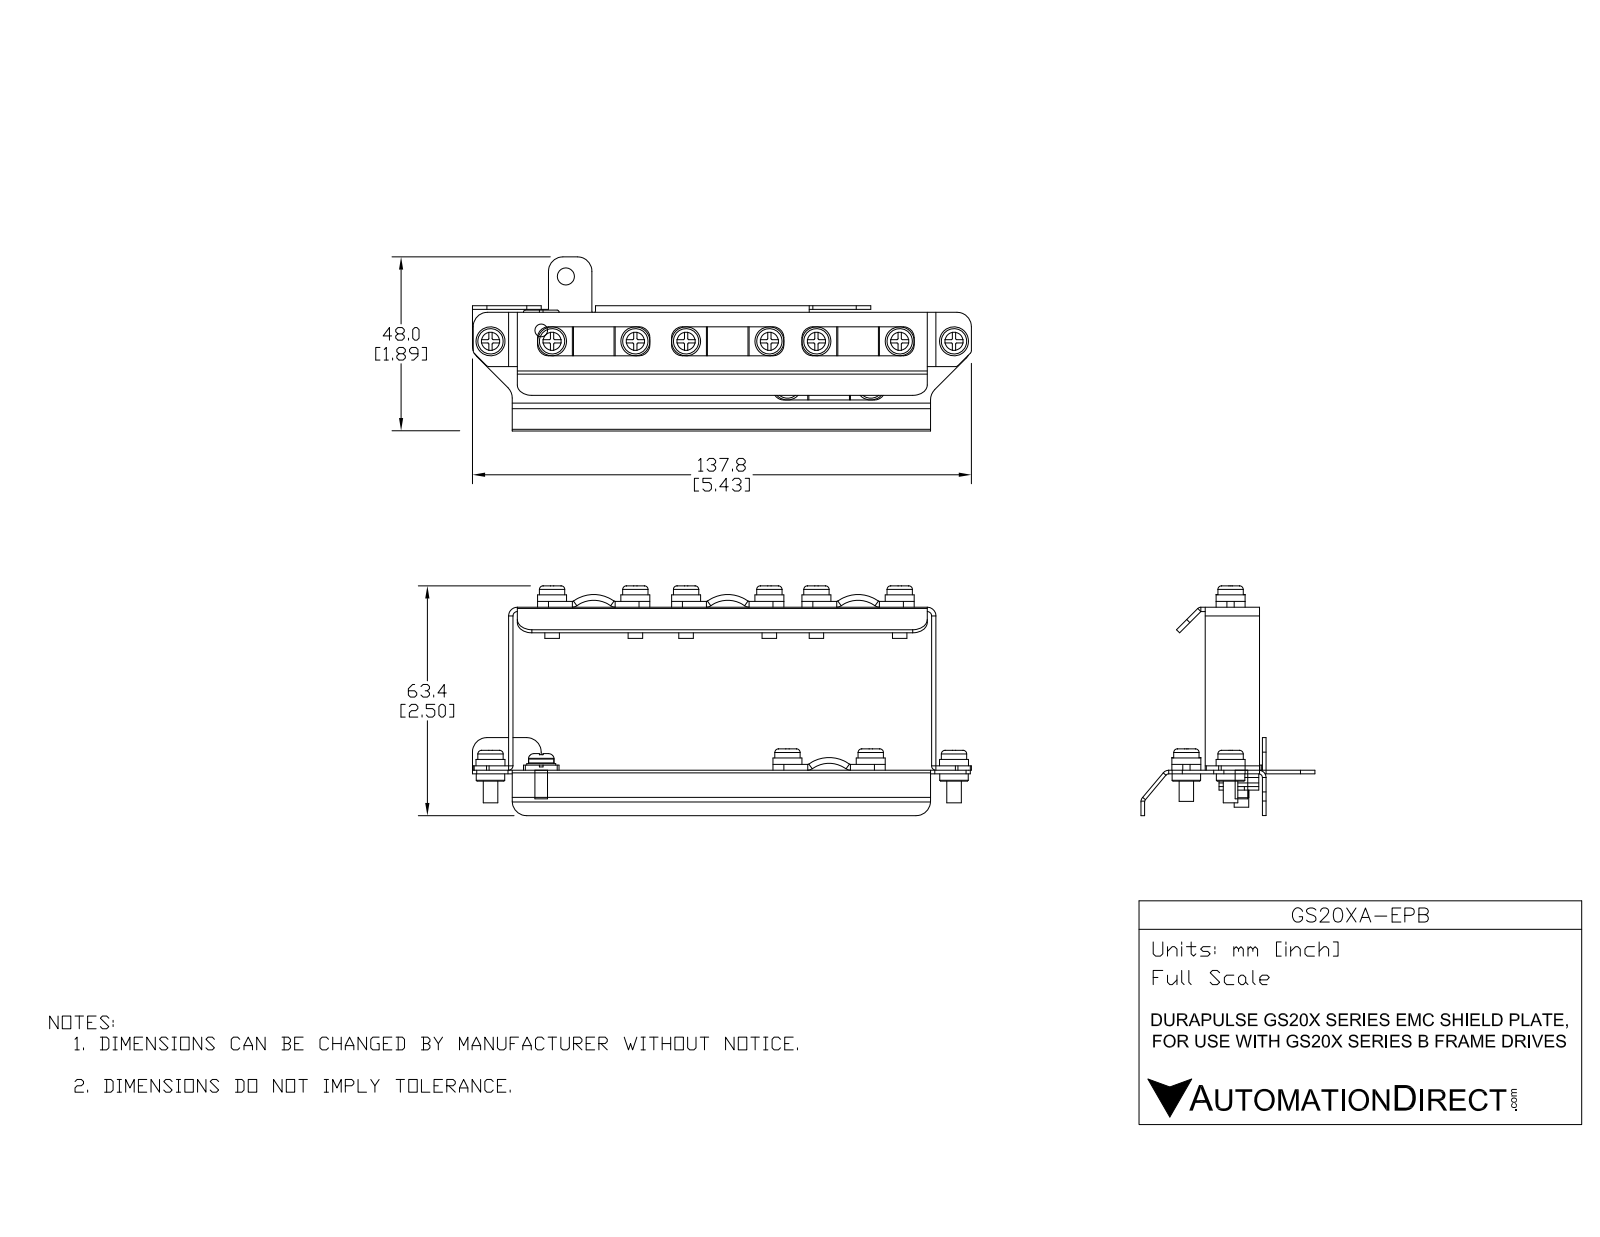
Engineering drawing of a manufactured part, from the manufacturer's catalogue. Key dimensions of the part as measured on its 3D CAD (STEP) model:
Part name (STEP PRODUCT): GS20XA-EPB
STEP written by: SolidWorks 2017 (AUTOMOTIVE_DESIGN)
Units: inches
Bodies: 30 solids, 987 faces (474 planar, 354 cylindrical, 159 other)
Overall size (bounding box): 5.425 × 2.658 × 1.892
Volume: 1.084 in³ · Surface area: 48.26 in²
Round holes (diameter × count): ⌀0.128 ×11, ⌀0.157 ×8, ⌀0.177 ×8, ⌀0.185 ×2, ⌀0.217 ×2, ⌀0.315 ×1
Round bosses / shafts (diameter × count): ⌀0.31 ×11, ⌀0.276 ×11, ⌀0.261 ×11, ⌀0.212 ×11, ⌀0.315 ×10, ⌀0.157 ×3, ⌀0.278 ×1
Partial cylindrical surfaces — rounded edges, fillets, slot ends (radius × count): R0.012 ×40, R0.157 ×22, R0.118 ×16, R0.02 ×14, R0.039 ×10, R0.083 ×8, R0.047 ×5, R0.079 ×5
Main face-to-face distances: 0.039, 0.047, 1.772, 1.724, 1.811, 1.764, 4.598, 1.321, 0.063, 4.646
Hole centre spacings: 0.906, 0.574, 1.202, 1.417, 1.457, 2.604, 2.874, 0.167
